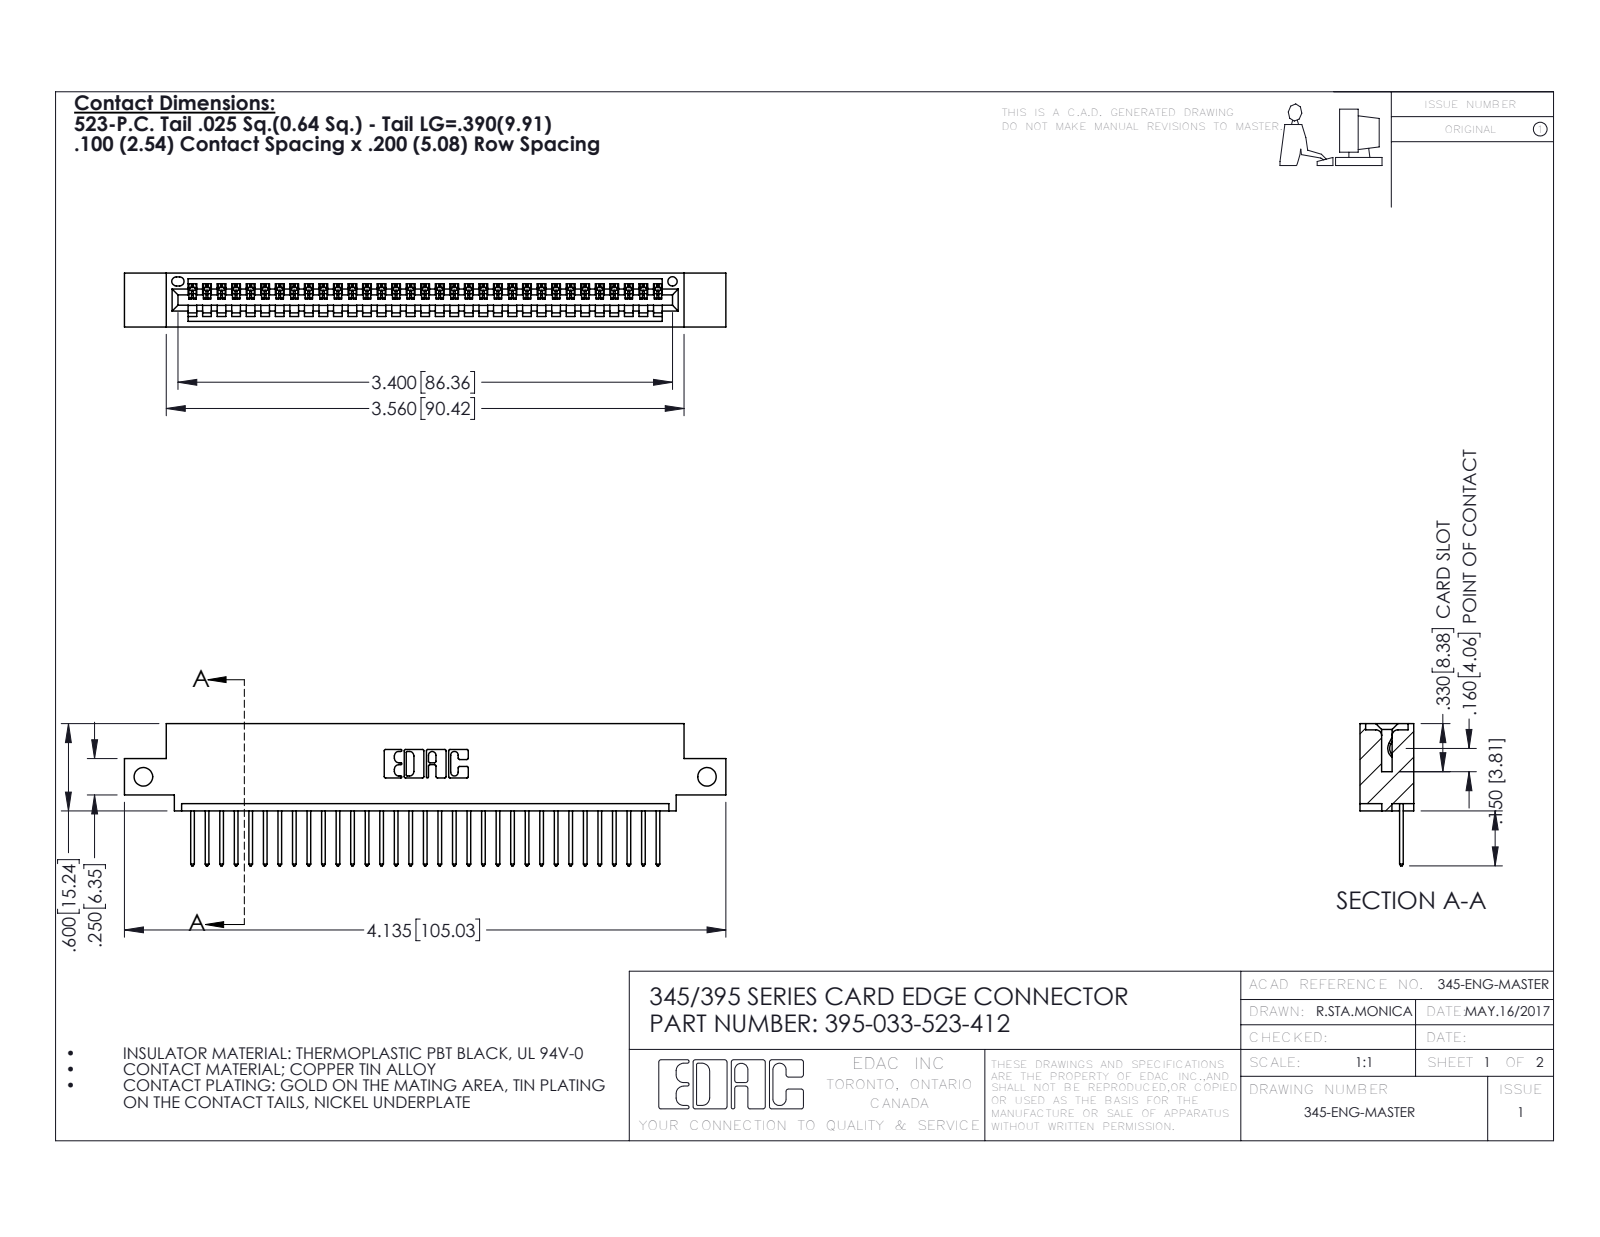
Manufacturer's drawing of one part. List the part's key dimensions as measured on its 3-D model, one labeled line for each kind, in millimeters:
Part name (STEP PRODUCT): 345-292-001_345-293-123; 395-033-523-412; 345 Part_0.110 Offset - Side Mount
STEP written by: SolidWorks 2016 (CONFIG_CONTROL_DESIGN)
Units: millimetres
Bodies: 34 solids, 2044 faces (1404 planar, 640 cylindrical, 0 other)
Overall size (bounding box): 105 × 24.8 × 9.4
Volume: 9 730 mm³ · Surface area: 12 780 mm²
Round holes (diameter × count): ⌀3.3 ×2, ⌀1.6 ×1
Partial cylindrical surfaces — rounded edges, fillets, slot ends (radius × count): R0.2 ×66, R0.3 ×66, R0.3 ×22, R0.2 ×6, R0.8 ×6, R0.7 ×3, R0.8 ×2, R1 ×2
Main face-to-face distances: 7.6, 1.8, 9.4, 5.1, 2.5, 6.9, 0.6, 5.7, 3.8, 1.8
Hole centre spacings: 98.4
